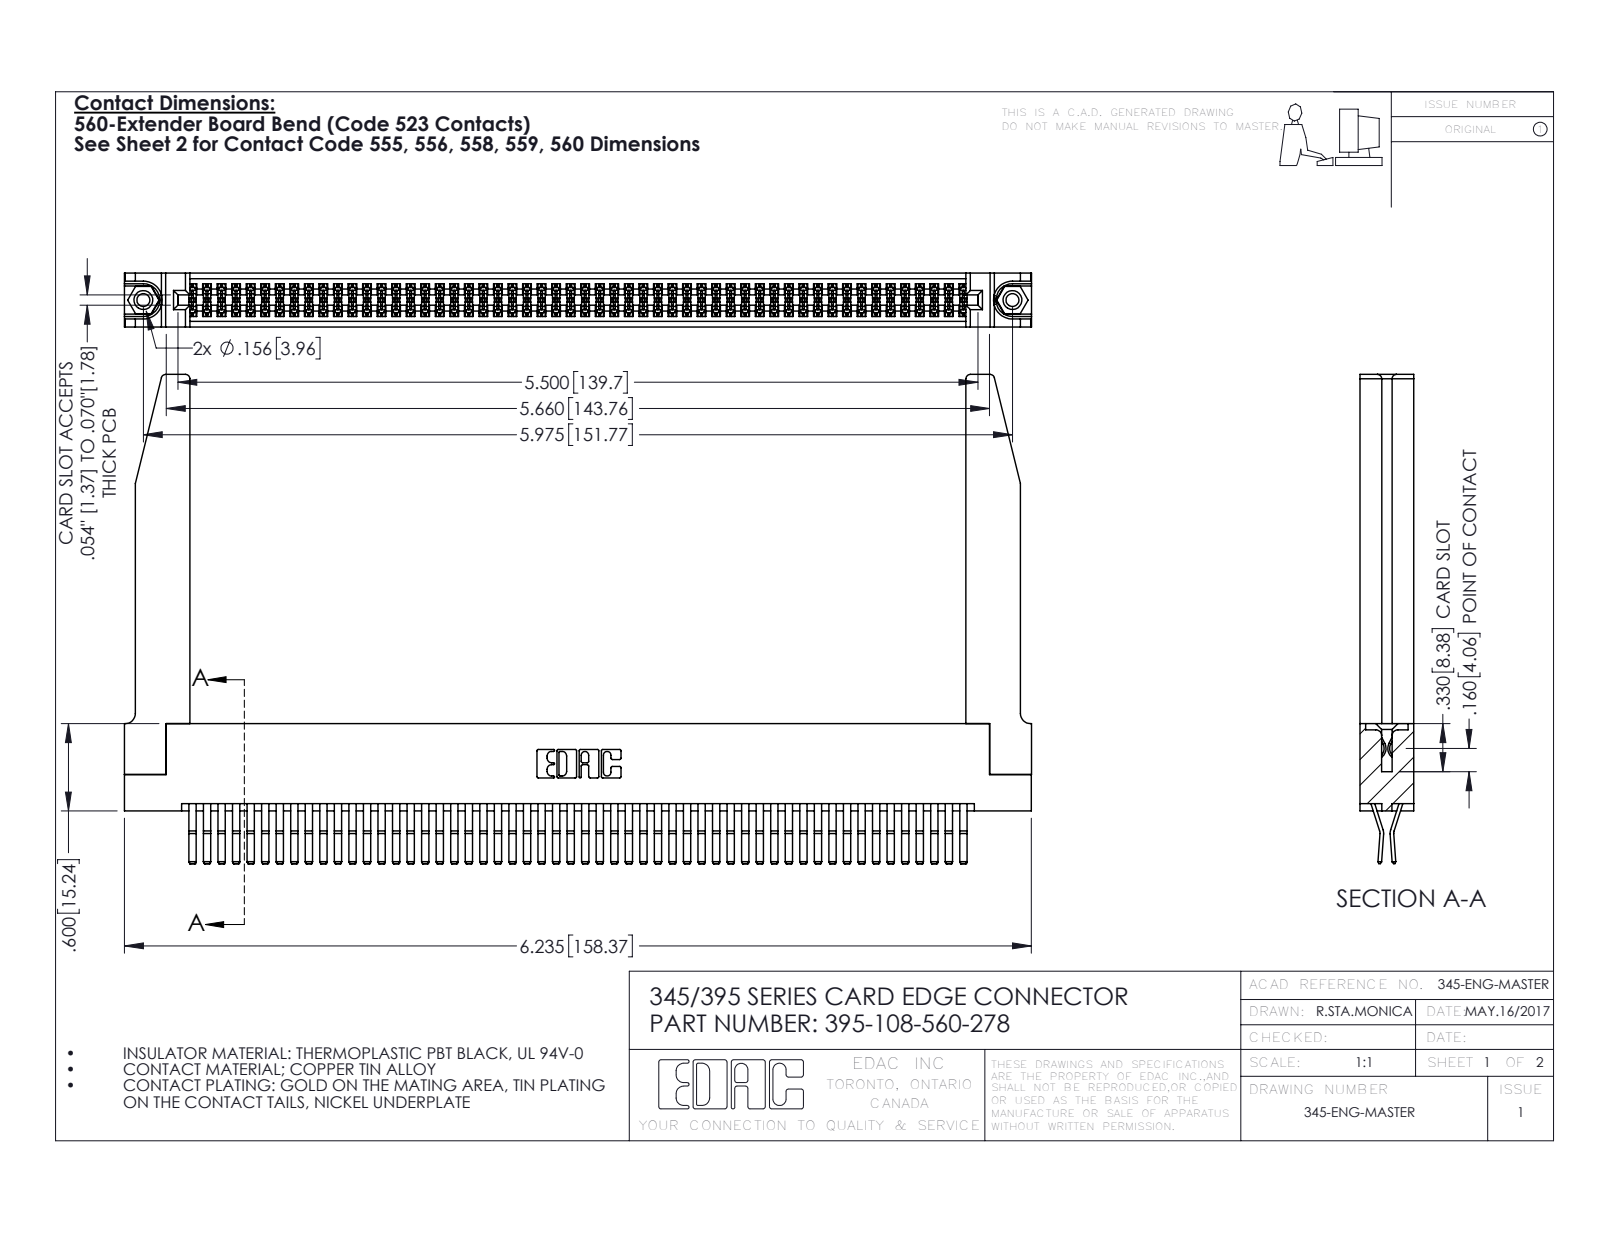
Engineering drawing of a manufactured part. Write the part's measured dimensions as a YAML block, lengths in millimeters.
part_name: "345 Part_Flush Mounting Lugs - 0.156 Dia-TH; 395-108-560-278; 345-292-001_560 Tail; 345-220-078_345-220-078 (+1 more)"
step_written_by: "SolidWorks 2016 (CONFIG_CONTROL_DESIGN)"
units: millimeters
bodies: {solids: 113, faces: 5976, planar: 3786, cylindrical: 2138, other: 52}
overall_size: [158.4, 85.4, 9.4]
volume: 23970
surface_area: 32850
round_holes:
  - {diameter: 2.3, count: 2}
  - {diameter: 3.2, count: 2}
  - {diameter: 4, count: 2}
  - {diameter: 1.6, count: 1}
round_bosses_or_shafts:
  - {diameter: 3.9, count: 2}
partial_cylinders:
  - {radius: 0.2, count: 162}
  - {radius: 0.3, count: 22}
  - {radius: 0.8, count: 8}
  - {radius: 0.2, count: 6}
  - {radius: 0.8, count: 6}
  - {radius: 0.7, count: 3}
  - {radius: 0.3, count: 2}
  - {radius: 0.4, count: 2}
face_to_face_distances: [1.8, 9.4, 7.6, 0.6, 5.1, 2.5, 6.9, 5.7, 4.4, 3.8]
hole_center_spacings: [6.9, 145.8, 151.8]
